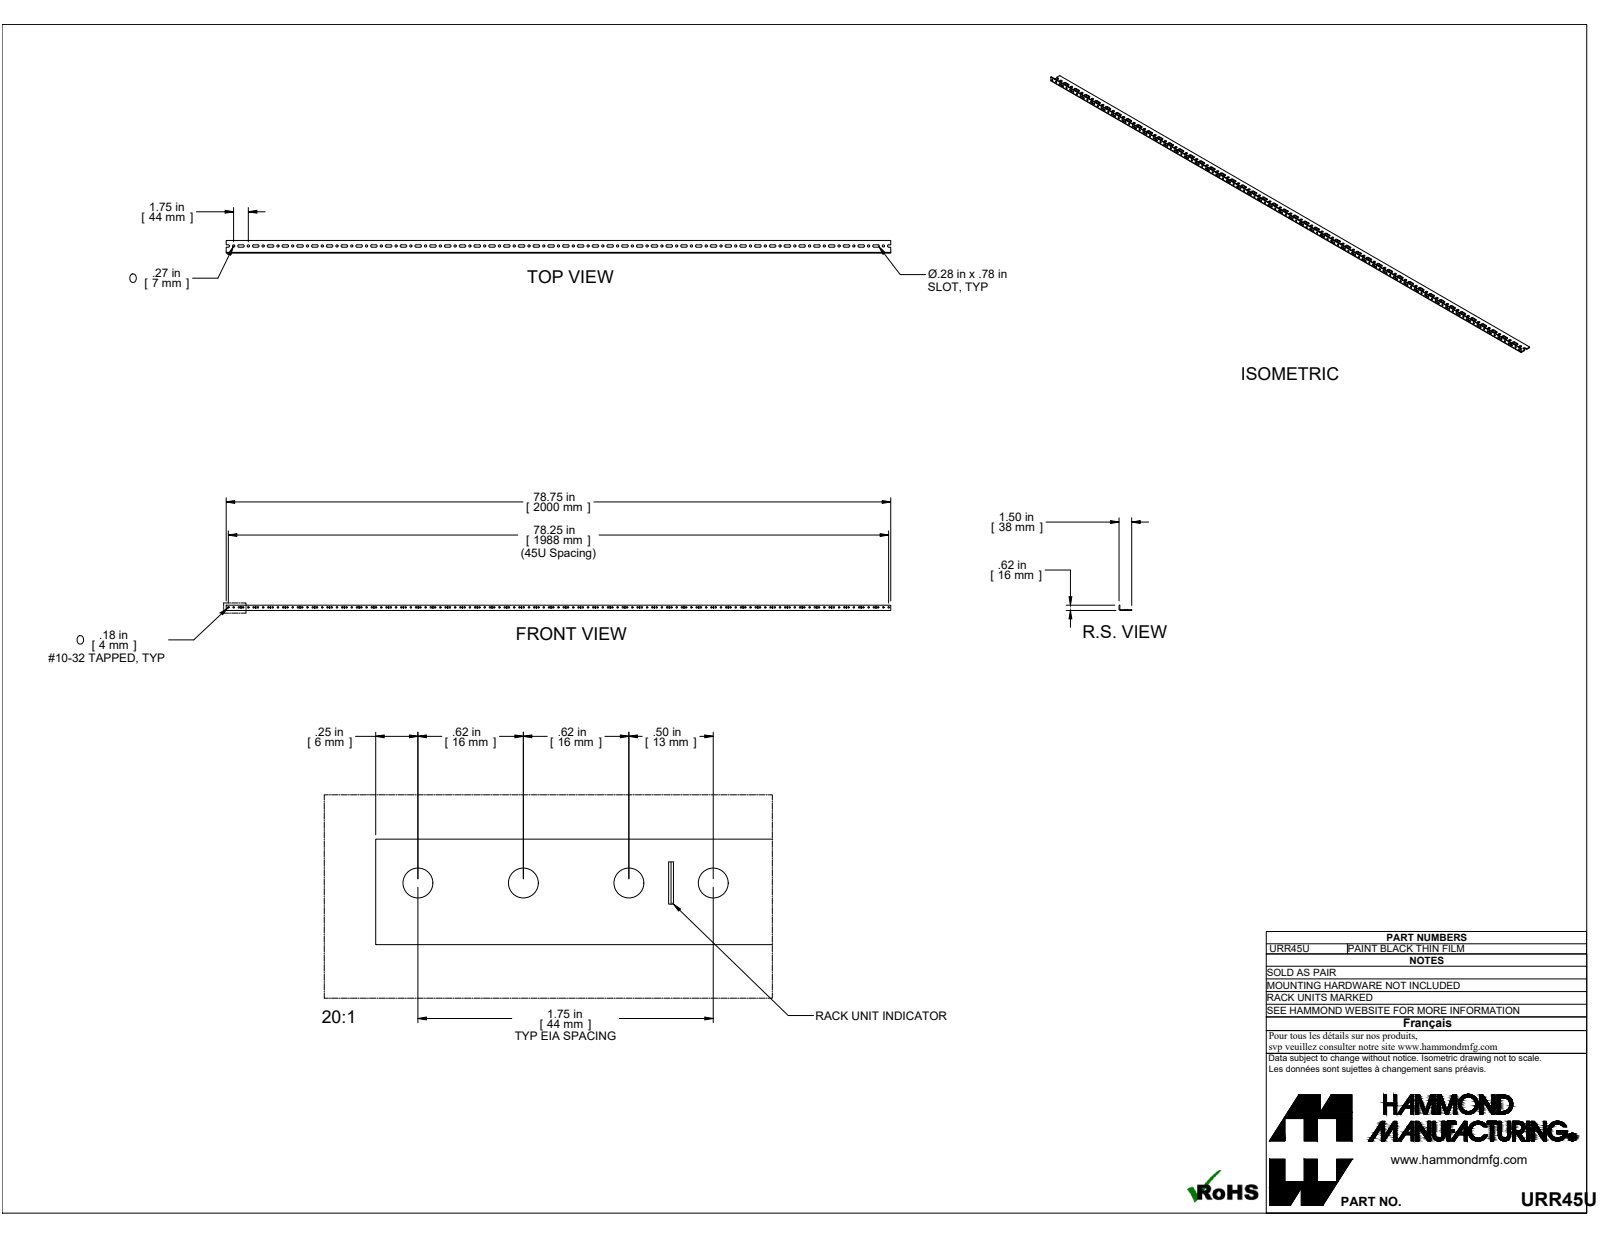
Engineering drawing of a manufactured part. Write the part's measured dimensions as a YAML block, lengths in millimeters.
part_name: "COM57213-45"
step_written_by: "ST-DEVELOPER v16.7 (AUTOMOTIVE_DESIGN)"
units: millimeters
bodies: {solids: 1, faces: 556, planar: 284, cylindrical: 272, other: 0}
overall_size: [2000.25, 38.1, 15.88]
volume: 220516
surface_area: 205003
round_holes:
  - {diameter: 4.5, count: 135}
  - {diameter: 6.76, count: 45}
partial_cylinders:
  - {radius: 3.57, count: 90}
  - {radius: 1.22, count: 1}
  - {radius: 3.63, count: 1}
face_to_face_distances: [2.41, 15.88, 13.47, 38.1, 35.69, 24.98, 22.57, 13.12, 17.84, 15.43]
hole_center_spacings: [88.9, 133.35, 44.45, 222.25, 177.8, 266.7, 311.15, 355.6]
